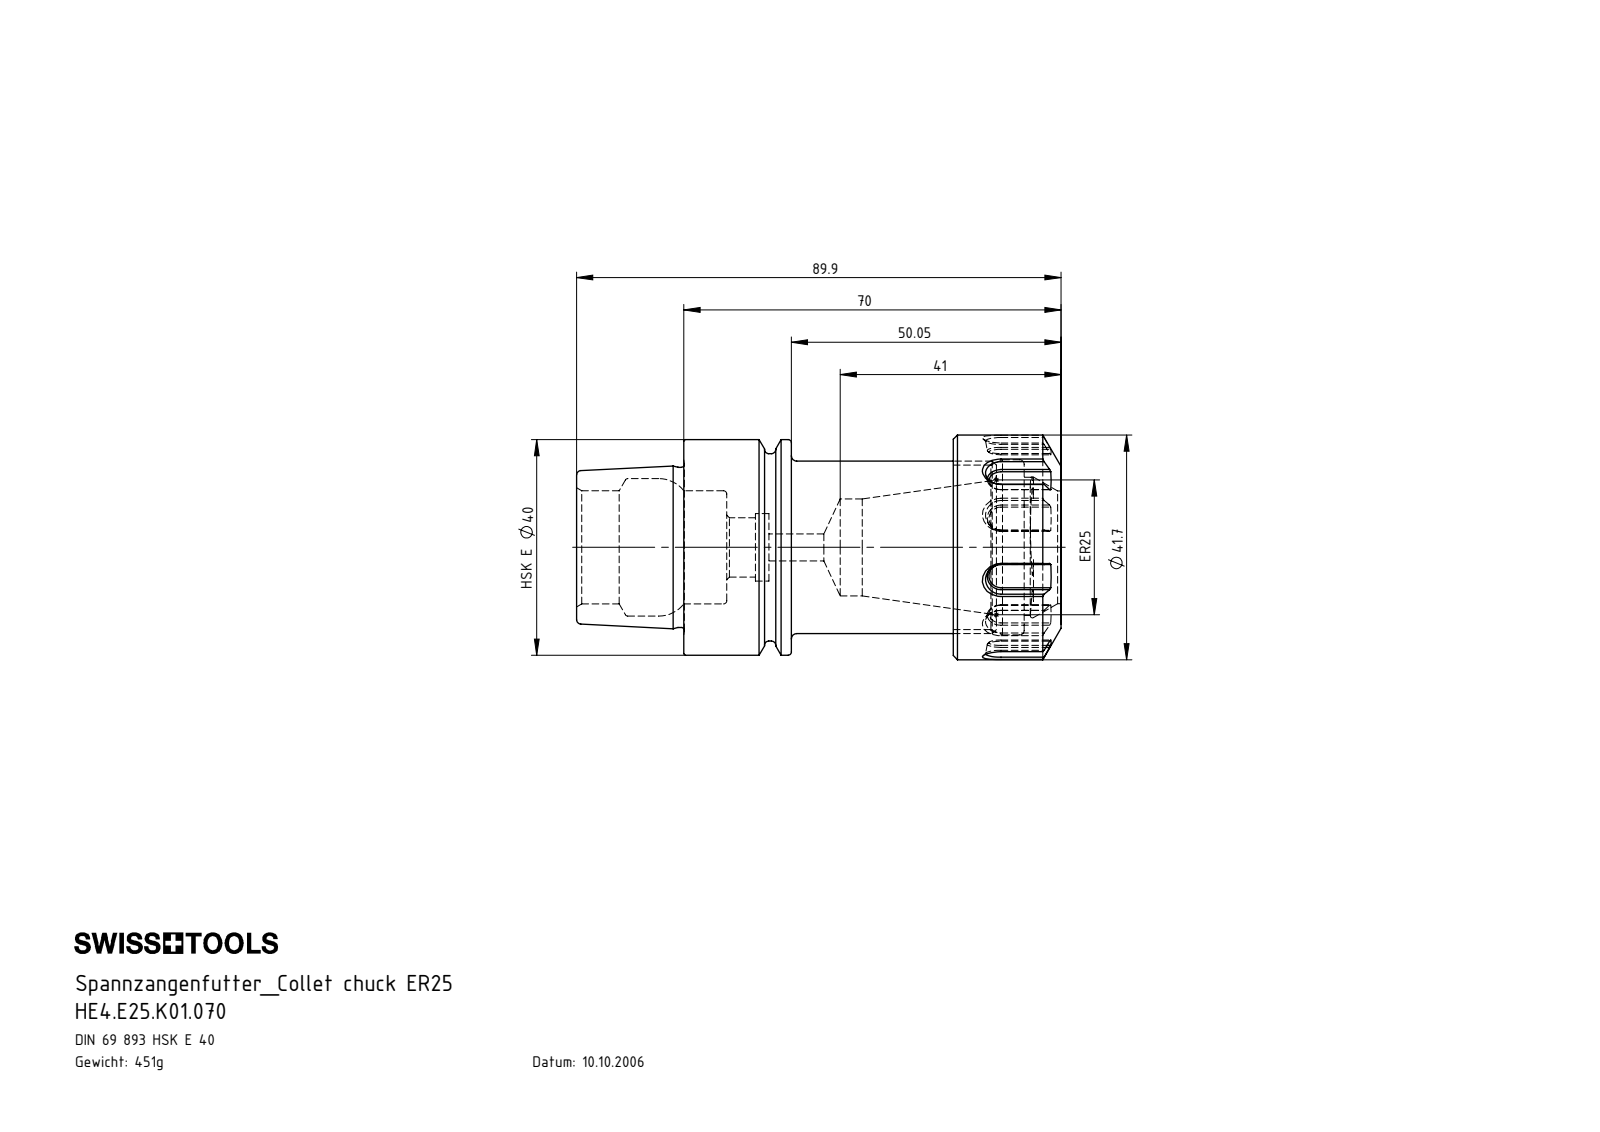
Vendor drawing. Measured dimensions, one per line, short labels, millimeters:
name: E25-ER1.001.020; HE4-E25.K01.070_A_Fertigbearbeitung; HE4.E25.K01.070
written by: SolidWorks 2017 (CONFIG_CONTROL_DESIGN)
unit: mm
bodies: 2 solids, 172 faces (59 planar, 35 cylindrical, 78 other)
size: 89.9 × 41.7 × 41.7
volume: 57 506 mm³; area: 21 293 mm²
holes: 1× ⌀5, 1× ⌀11, 1× ⌀12.5, 1× ⌀18, 1× ⌀20.9, 1× ⌀21, 1× ⌀25.5, 1× ⌀30.5, 1× ⌀32.5
bosses: 1× ⌀41.7, 1× ⌀40, 1× ⌀34.75, 1× ⌀32, 1× ⌀29.71
rounds: 2× R12.17
face distances: 50.05, 50, 12, 70, 20, 19.95, 30.05, 63.15, 43.2, 13.15
